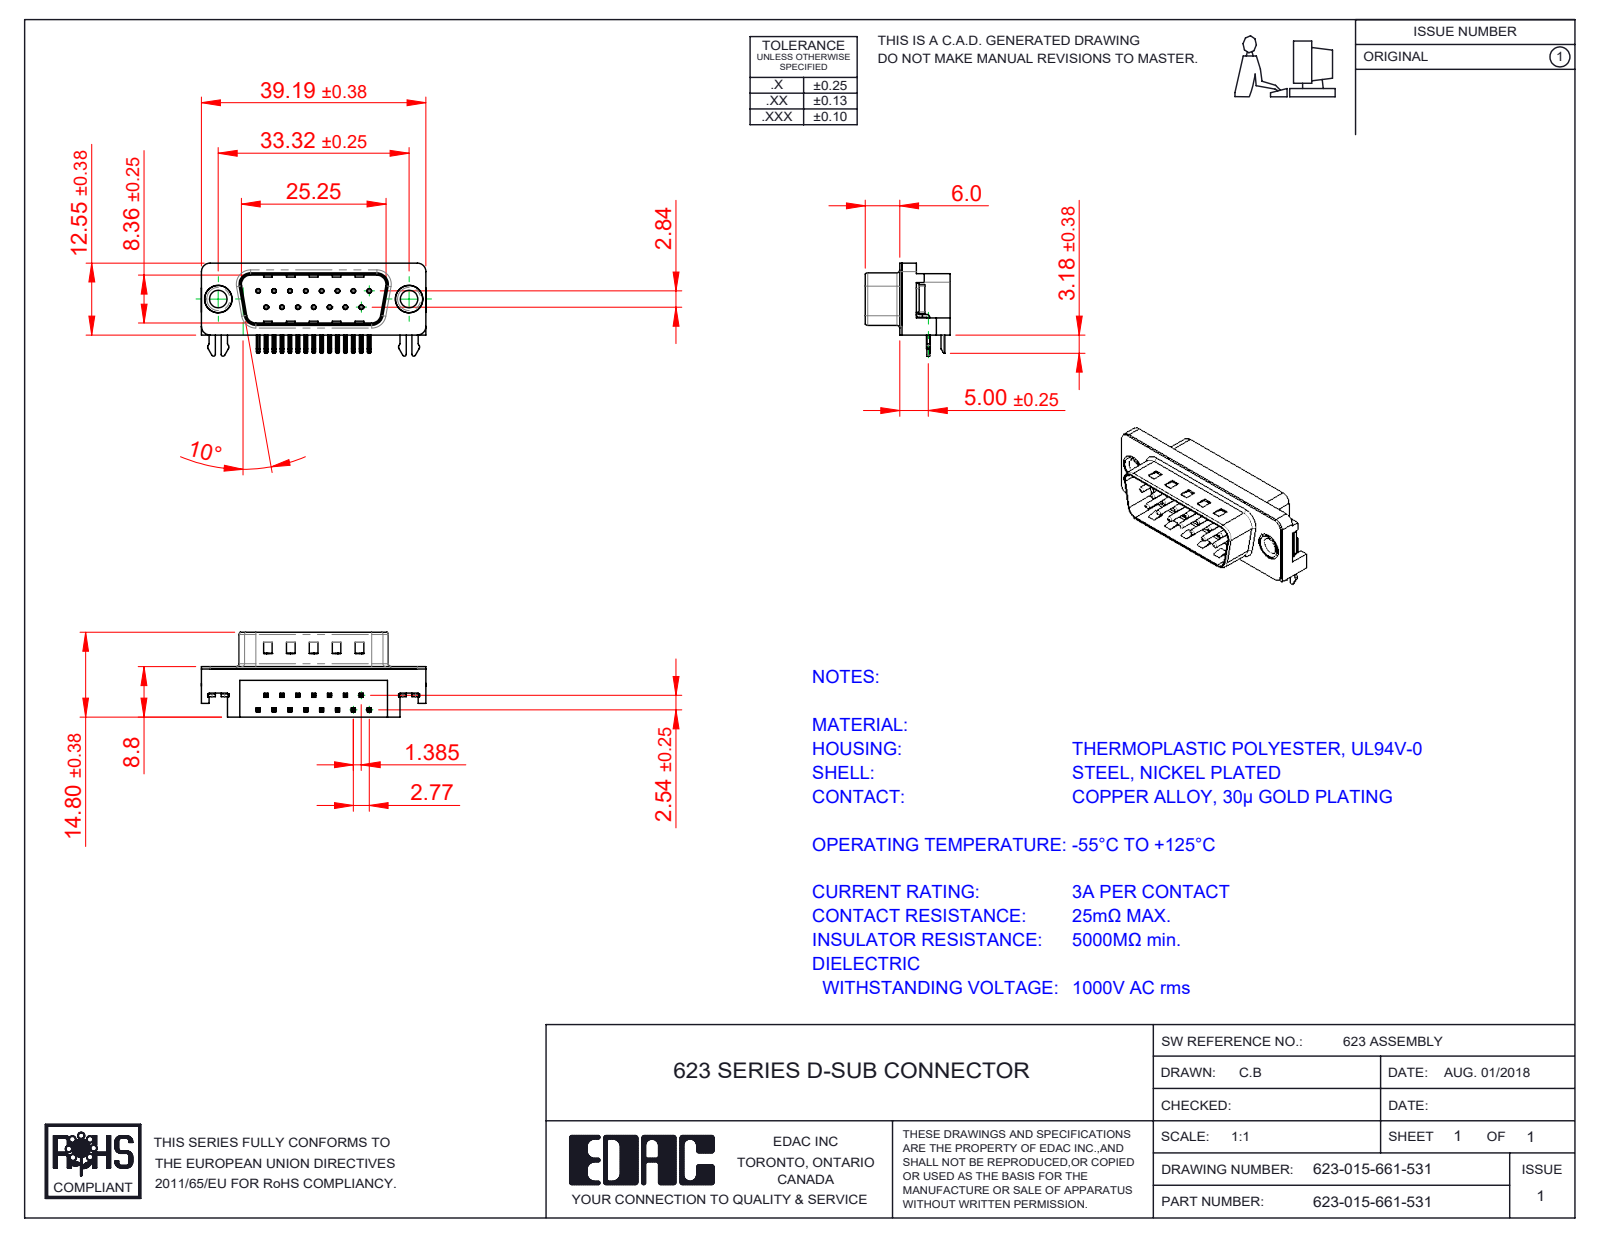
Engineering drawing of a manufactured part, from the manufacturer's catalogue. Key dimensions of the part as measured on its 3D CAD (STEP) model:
Part name (STEP PRODUCT): 623 Thru Hole Rivet; 623 Contact Top; 623 Contact Bottom; 623 Shell_15 Socket (+3 more)
STEP written by: SolidWorks 2016 (CONFIG_CONTROL_DESIGN)
Units: millimetres
Bodies: 21 solids, 1459 faces (921 planar, 421 cylindrical, 117 other)
Overall size (bounding box): 39.22 × 16.25 × 14.8
Volume: 3 315 mm³ · Surface area: 4 923 mm²
Round holes (diameter × count): ⌀0.35 ×15, ⌀0.8 ×15, ⌀3.05 ×2, ⌀4 ×2, ⌀4.8 ×2, ⌀5 ×2
Round bosses / shafts (diameter × count): ⌀0.75 ×15, ⌀4.9 ×2, ⌀4.75 ×2, ⌀3.85 ×2
Partial cylindrical surfaces — rounded edges, fillets, slot ends (radius × count): R0.25 ×68, R0.12 ×30, R0.5 ×14, R1 ×8, R1.5 ×6, R0.32 ×4, R0.9 ×4, R1.6 ×4
Main face-to-face distances: 0.4, 8.4, 2.1, 1.7, 8.8, 10.46, 10.86, 8.76, 5.9, 2.9
Hole centre spacings: 3.16, 2.77, 5.54, 8.31, 11.08, 5.03, 5.04, 7.48
